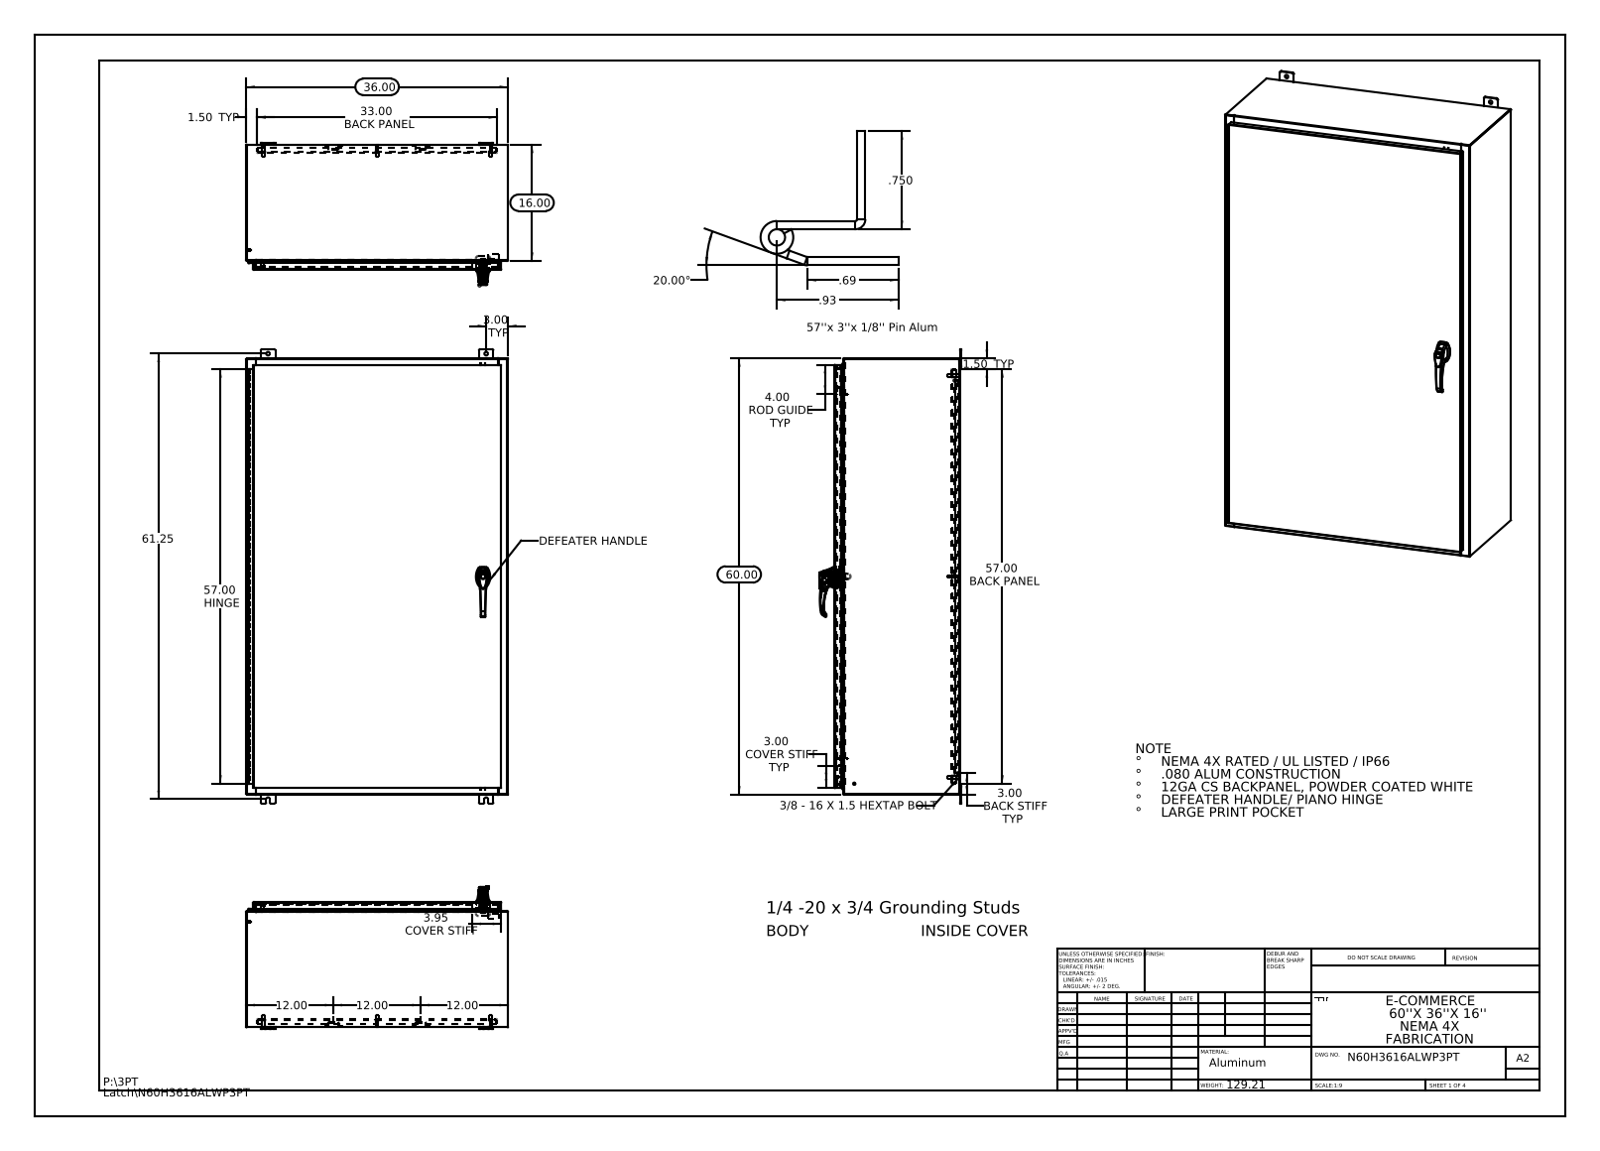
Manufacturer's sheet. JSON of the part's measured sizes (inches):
{"part_name": "297026; N60H3616ALWP3PT Bottom; N60H3616ALWP3PT 263033_Industrilas; N60H3616ALWP3PT Hinge Enclosure Side2 (+8 more)", "step_written_by": "SolidWorks 2013 (CONFIG_CONTROL_DESIGN)", "units": "inches", "bodies": {"solids": 51, "faces": 3688, "planar": 1453, "cylindrical": 1449, "other": 786}, "overall_size": [62.5, 36, 19.495], "volume_in3": 855.6, "surface_area_in2": 21358, "round_holes": [[0.5, 12], [0.25, 10], [0.138, 3], [0.161, 3], [0.079, 2], [0.203, 2], [0.313, 2], [0.437, 2], [0.125, 1], [0.125, 1], [0.197, 1], [0.276, 1]], "round_bosses_or_shafts": [[0.157, 10], [0.14, 10], [0.625, 8], [0.375, 8], [0.33, 8], [0.315, 3], [0.236, 3], [1.181, 1]], "partial_cylinders_radius": [[0.118, 37], [0.013, 34], [0.006, 33], [0.088, 28], [0.19, 24], [0.039, 15], [0.028, 12], [0.008, 6]], "face_to_face_distances": [0.075, 17.126, 17.051, 0.104, 17.201, 35.925, 1, 16.126, 1.075, 16.051], "hole_center_spacings": [23.354, 25.662, 27.625, 41.709, 57.417, 30.975, 31.25, 55.25]}
